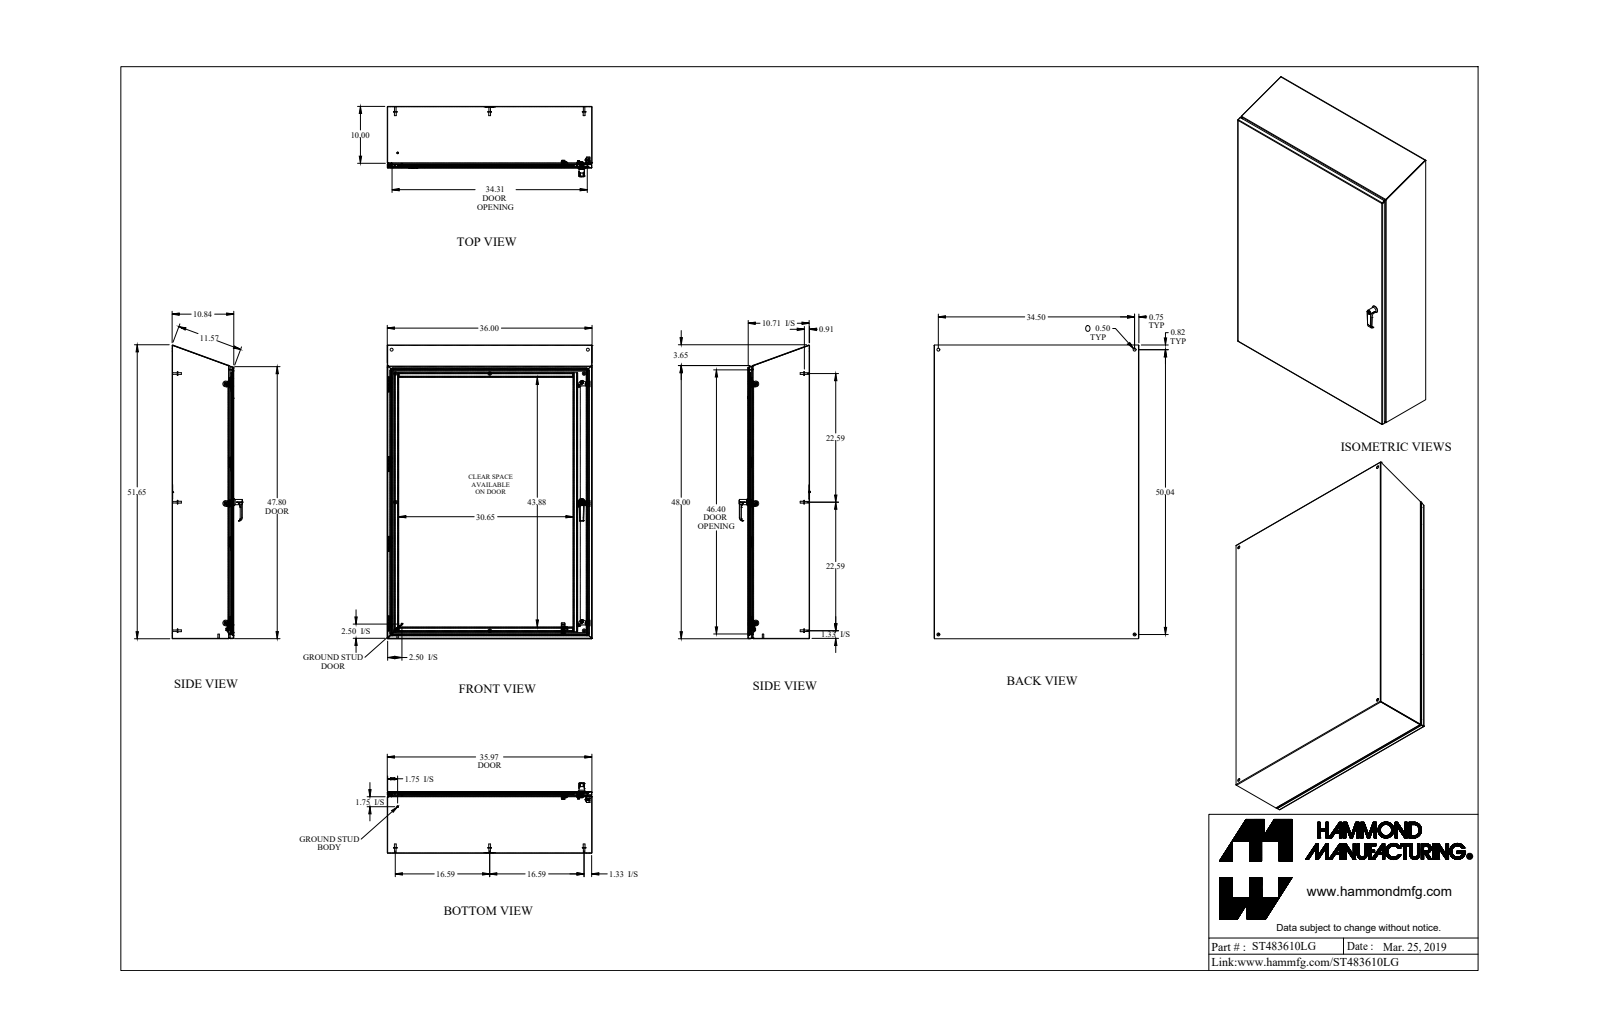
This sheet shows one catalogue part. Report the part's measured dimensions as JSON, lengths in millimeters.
{"part_name": "ST483610LG", "step_written_by": "SolidWorks 2018 (AUTOMOTIVE_DESIGN)", "units": "millimeters", "bodies": {"solids": 64, "faces": 1732, "planar": 765, "cylindrical": 642, "other": 325}, "overall_size": [1310.8, 914.4, 314.1], "volume_mm3": 7266000, "surface_area_mm2": 8009000, "round_holes": [[4.5, 6], [5, 4], [12.7, 4], [6.4, 3], [6.7, 3], [10.5, 3], [6.5, 2], [8, 2], [10, 2], [4.4, 1], [6.1, 1], [6.1, 1]], "round_bosses_or_shafts": [[8, 9], [6.9, 9], [15.9, 7], [6.4, 7], [9.5, 6], [4, 6], [25.4, 3], [15.9, 3]], "partial_cylinders_radius": [[1.1, 24], [2.1, 24], [0.9, 19], [2.7, 18], [1.6, 17], [0.8, 15], [2.4, 10], [0.4, 9]], "face_to_face_distances": [1.8, 271.6, 273.4, 1.8, 275.3, 273.4, 912.6, 910.7, 914.4, 21.3], "hole_center_spacings": [533.4, 1066.8, 20, 876.3, 1270.9, 1543.7, 20, 59.9]}
